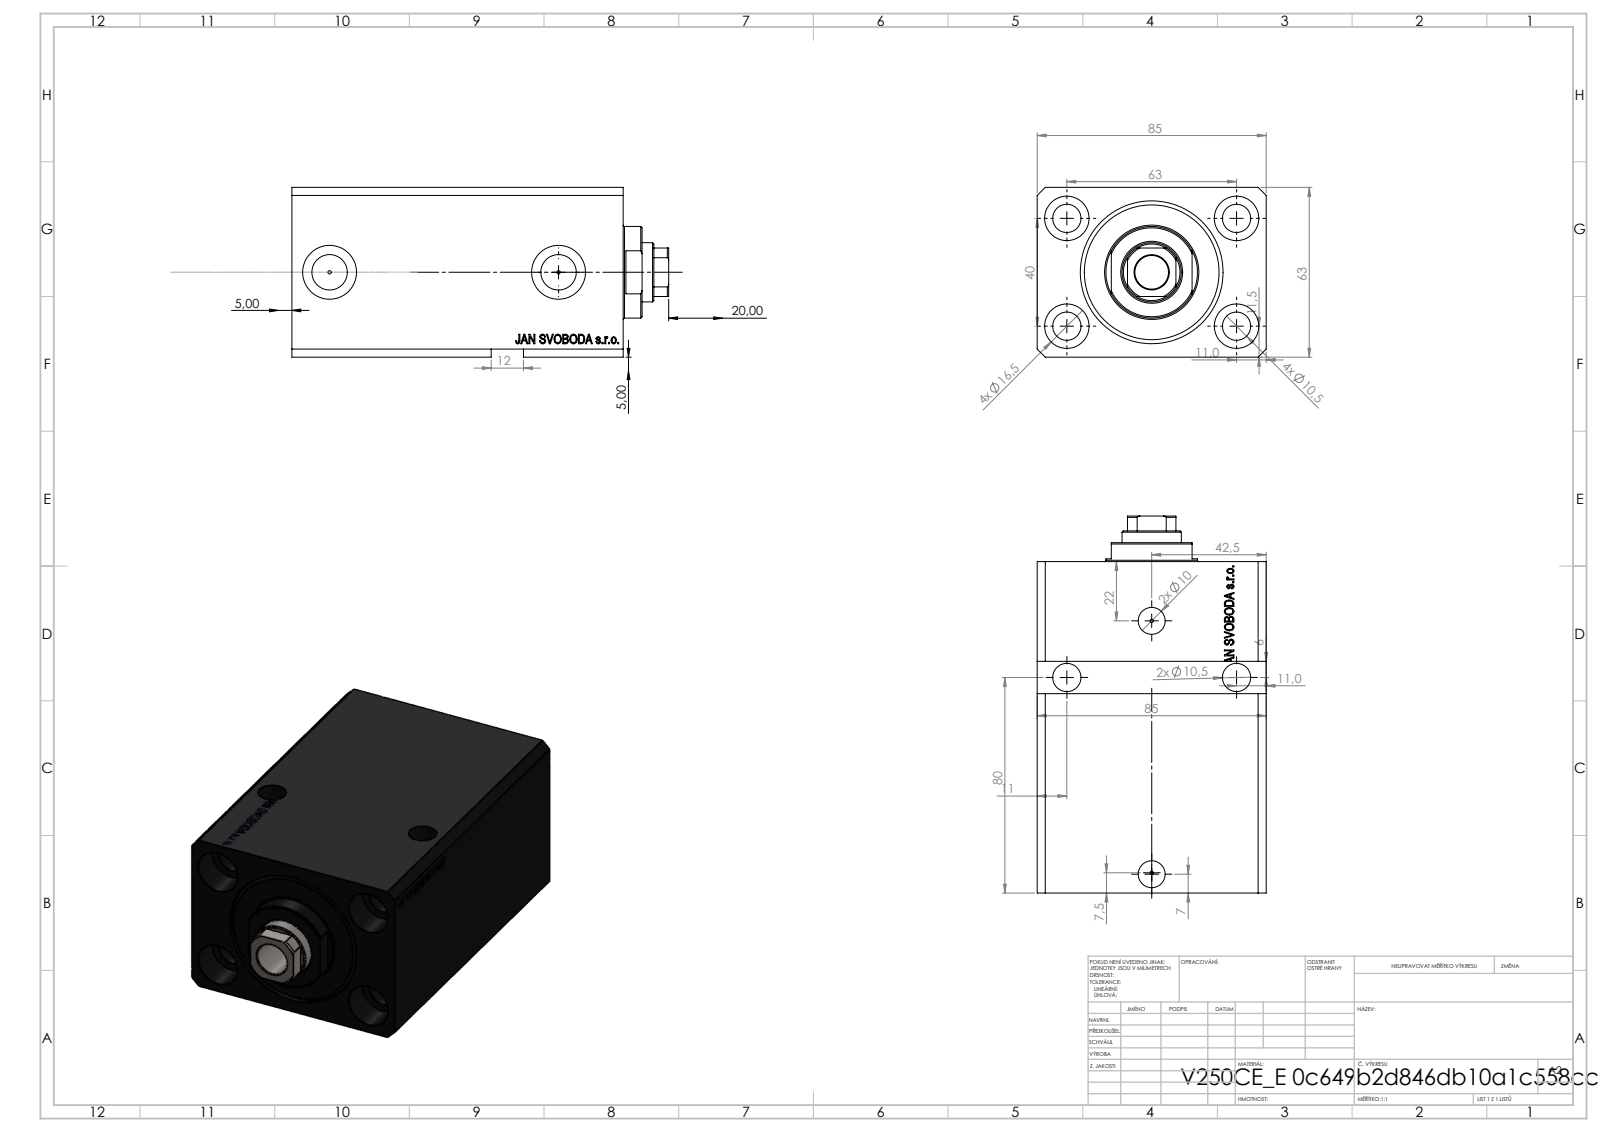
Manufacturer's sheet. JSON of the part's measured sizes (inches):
{"part_name": "V250CE_VC_E; V250CE_E_Body; V250CE_C_VCP", "step_written_by": "SolidWorks 2019 (CONFIG_CONTROL_DESIGN)", "units": "inches", "bodies": {"solids": 3, "faces": 937, "planar": 459, "cylindrical": 104, "other": 374}, "overall_size": [5.512, 3.346, 2.48], "volume_in3": 33.12, "surface_area_in2": 167, "round_holes": [[0.413, 8], [0.049, 4], [0.65, 4], [0.394, 2], [0.518, 2], [0.787, 2], [0.492, 1], [0.866, 1], [1.575, 1], [2.087, 1]], "round_bosses_or_shafts": [[1.339, 1]], "partial_cylinders_radius": [[0.413, 1]], "face_to_face_distances": [2.48, 3.346, 4.843, 0.669, 4.173, 0.449, 3.724, 4.394, 2.205, 0.433], "hole_center_spacings": [1.469, 2.48, 1.491, 1.575, 1.646, 1.659, 1.772, 2.879]}
